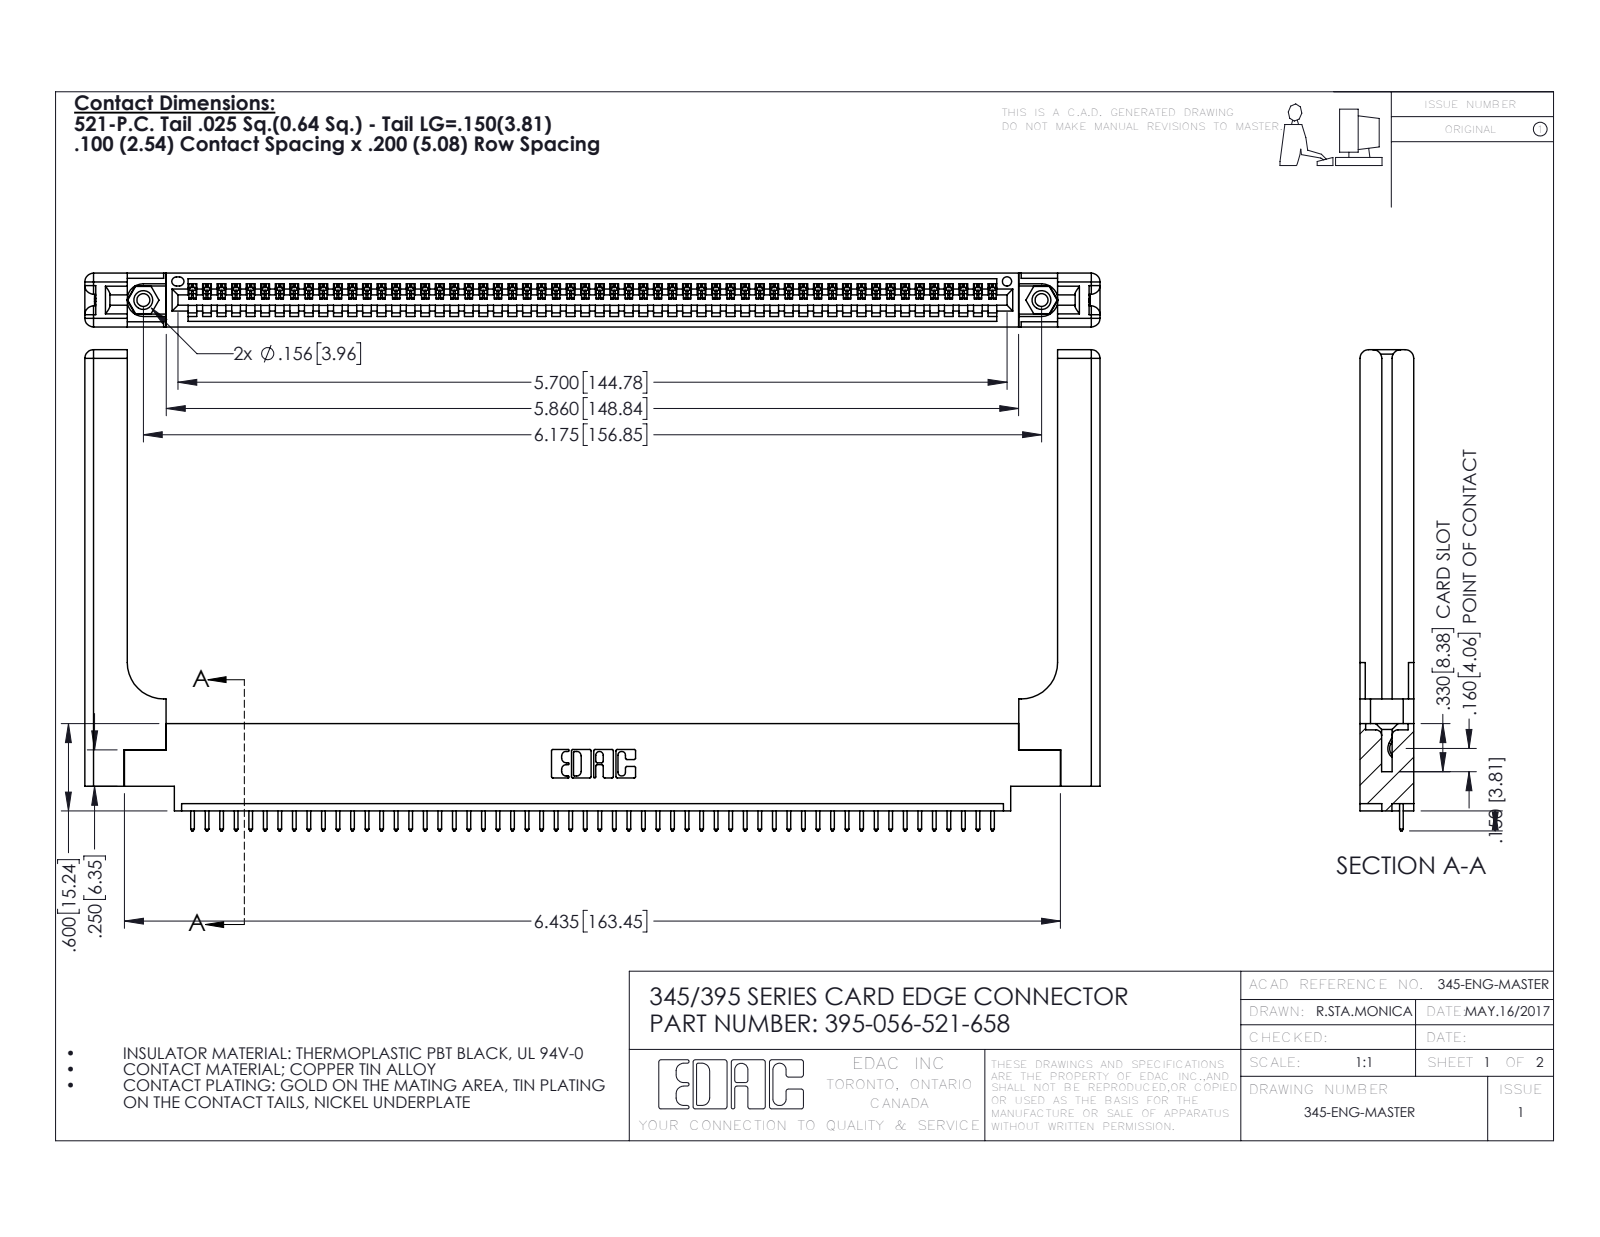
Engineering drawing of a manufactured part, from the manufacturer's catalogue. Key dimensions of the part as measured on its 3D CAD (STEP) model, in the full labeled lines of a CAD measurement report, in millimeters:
Part name (STEP PRODUCT): 345-220-058_345-220-058; 395-056-521-658; 345-250-001_345-250-001-102; 345-292-001_345-293-121 (+1 more)
STEP written by: SolidWorks 2016 (CONFIG_CONTROL_DESIGN)
Units: millimetres
Bodies: 61 solids, 3634 faces (2472 planar, 1102 cylindrical, 60 other)
Overall size (bounding box): 177.3 × 84 × 9.4
Volume: 25 190 mm³ · Surface area: 27 160 mm²
Round holes (diameter × count): ⌀2.3 ×2, ⌀3.2 ×2, ⌀4 ×2, ⌀1.6 ×1
Round bosses / shafts (diameter × count): ⌀3.9 ×2
Partial cylindrical surfaces — rounded edges, fillets, slot ends (radius × count): R0.2 ×112, R0.3 ×112, R0.3 ×22, R1.5 ×16, R0.2 ×6, R0.8 ×6, R0.7 ×3, R0.8 ×2
Main face-to-face distances: 9.4, 1.8, 7.6, 2.5, 6.9, 0.6, 5.1, 5.7, 3.8, 3.8
Hole centre spacings: 6.9, 150.9, 156.8
